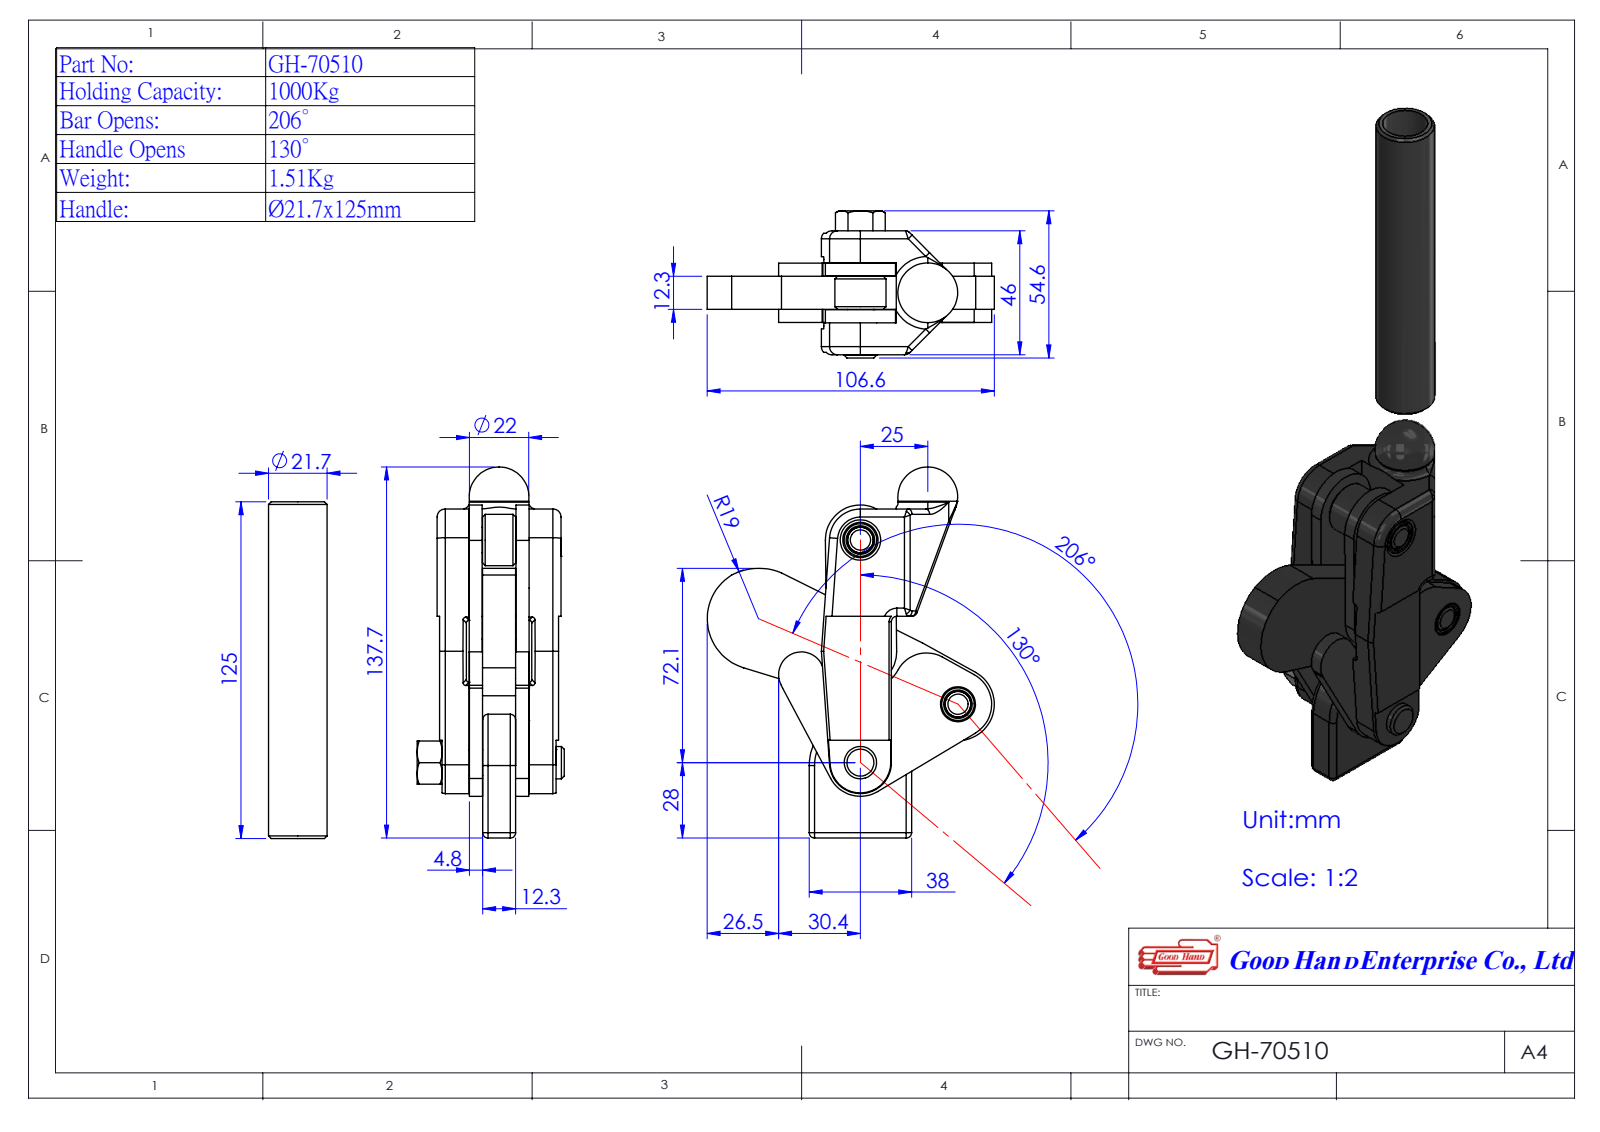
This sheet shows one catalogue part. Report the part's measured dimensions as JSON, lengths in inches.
{"part_name": "3700808-1^GH-70510(簡化); Group5^GH-70510(簡化); Group3^GH-70510(簡化); 3700829-1^GH-70510(簡化) (+3 more)", "step_written_by": "SolidWorks 2016 (AUTOMOTIVE_DESIGN)", "units": "inches", "bodies": {"solids": 6, "faces": 166, "planar": 71, "cylindrical": 68, "other": 27}, "overall_size": [10.333, 4.176, 2.15], "volume_in3": 12.72, "surface_area_in2": 115.5, "round_holes": [[0.374, 4], [0.394, 1], [0.677, 1]], "round_bosses_or_shafts": [[0.865, 1], [0.854, 1], [0.748, 1], [0.472, 1], [0.374, 1]], "partial_cylinders_radius": [[0.079, 2], [0.453, 2], [0.492, 2], [0.512, 2], [0.748, 2], [0.332, 1], [0.437, 1], [0.472, 1]], "face_to_face_distances": [0.68, 0.191, 0.484, 0.675, 0.68, 0.196, 0.196, 0.876, 0.192, 0.674], "hole_center_spacings": [1.603, 1.618, 1.624, 1.634, 1.661, 1.665, 2.791, 3.252]}
